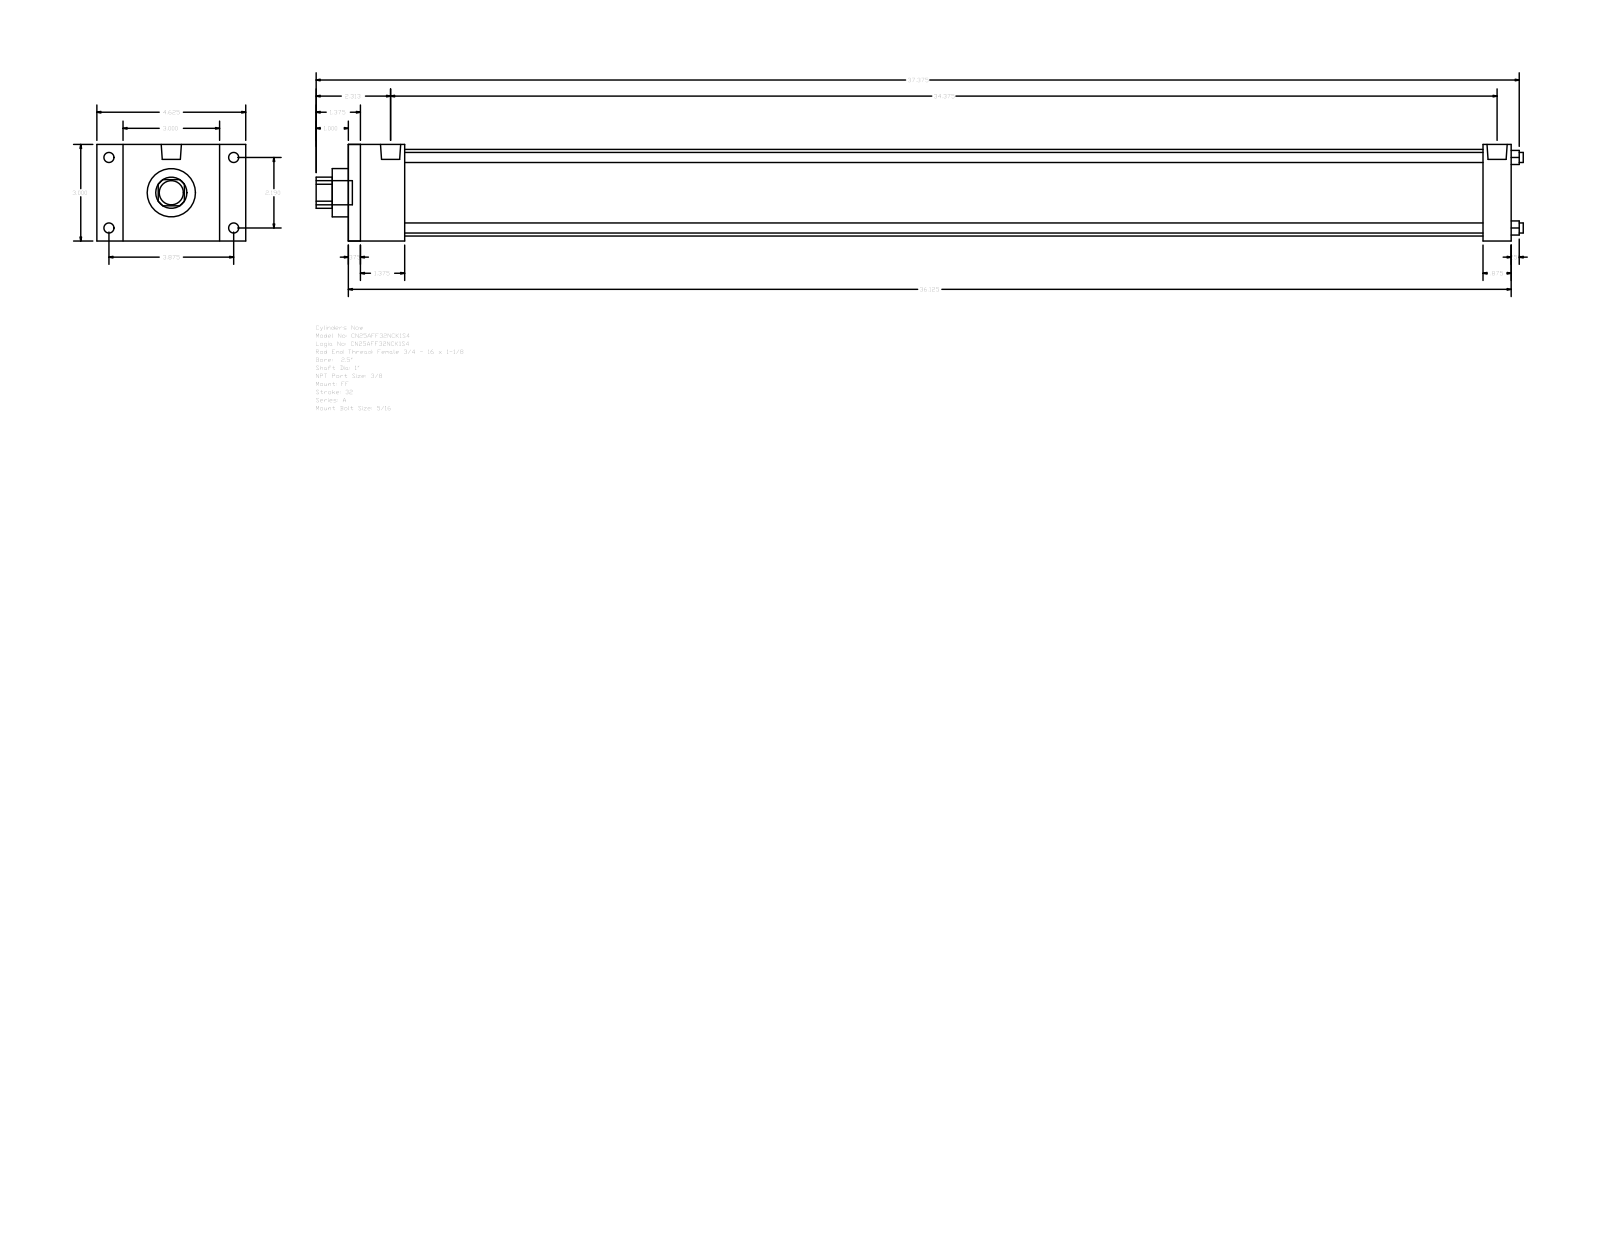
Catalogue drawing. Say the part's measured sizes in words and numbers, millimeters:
The part is named "A_FF__0250_1". Its 3-D file was written by "GSSL Pune (CONFIG_CONTROL_DESIGN)". It is 0 solids with 92 faces: 64 planar, 28 cylindrical and 0 other. Overall it measures 952.5 by 117.47 by 76.2 millimeters. Round holes: 4 of diameter 7.94, 1 of diameter 25.4, 1 of diameter 38.1, 1 of diameter 68.33. Round bosses or shafts: 4 of diameter 7.94, 4 of diameter 5.56, 2 of diameter 15.93, 1 of diameter 19.05. Partial cylindrical surfaces (rounded edges, fillets, slot ends): 1 of radius 12.29. The main face-to-face distances are 76.2, 917.58, 9.52, 908.06, 44.45, 895.35, 34.93, 885.83, 850.9, 873.13. The hole center spacings are 39.33, 55.62, 78.66.
